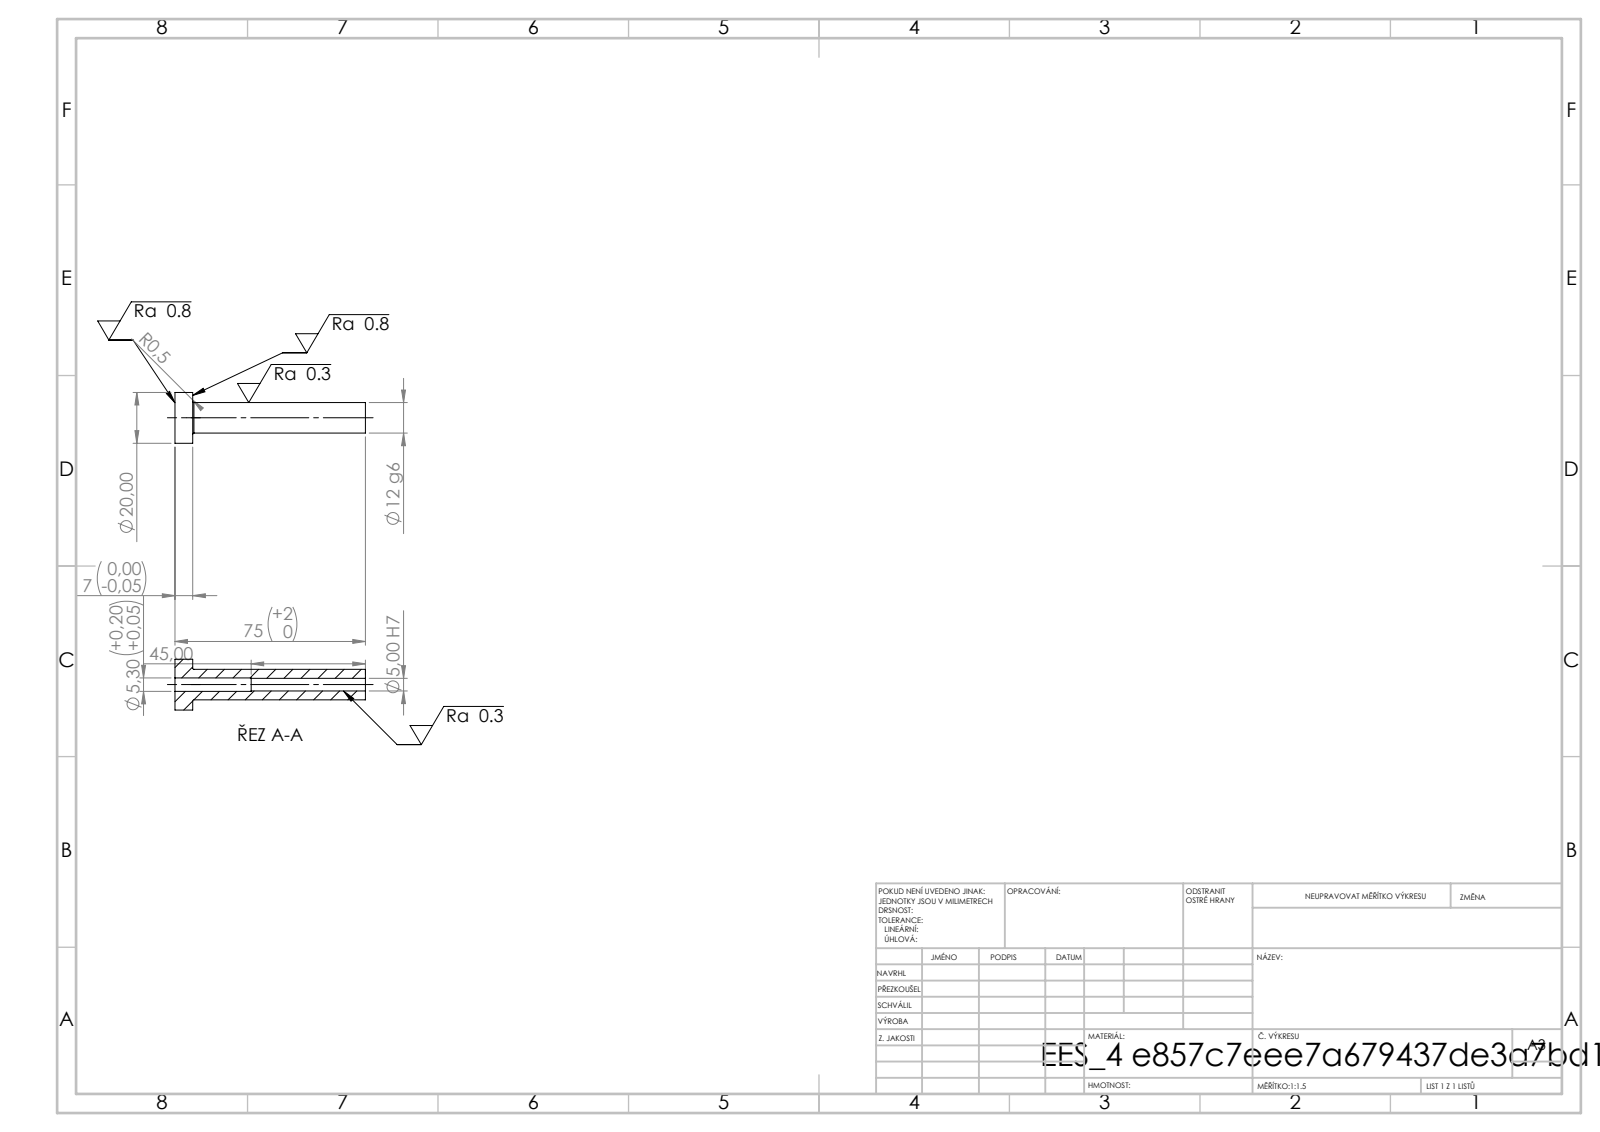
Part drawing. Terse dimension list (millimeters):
written by: SolidWorks 2019 (CONFIG_CONTROL_DESIGN)
unit: mm
bodies: 1 solid, 14 faces (4 planar, 8 cylindrical, 2 other)
size: 75 × 20 × 20
volume: 8 346 mm³; area: 4 791 mm²
holes: 1× ⌀5, 1× ⌀5.3
bosses: 1× ⌀20, 1× ⌀12
face distances: 7, 75, 68, 30, 23, 45
